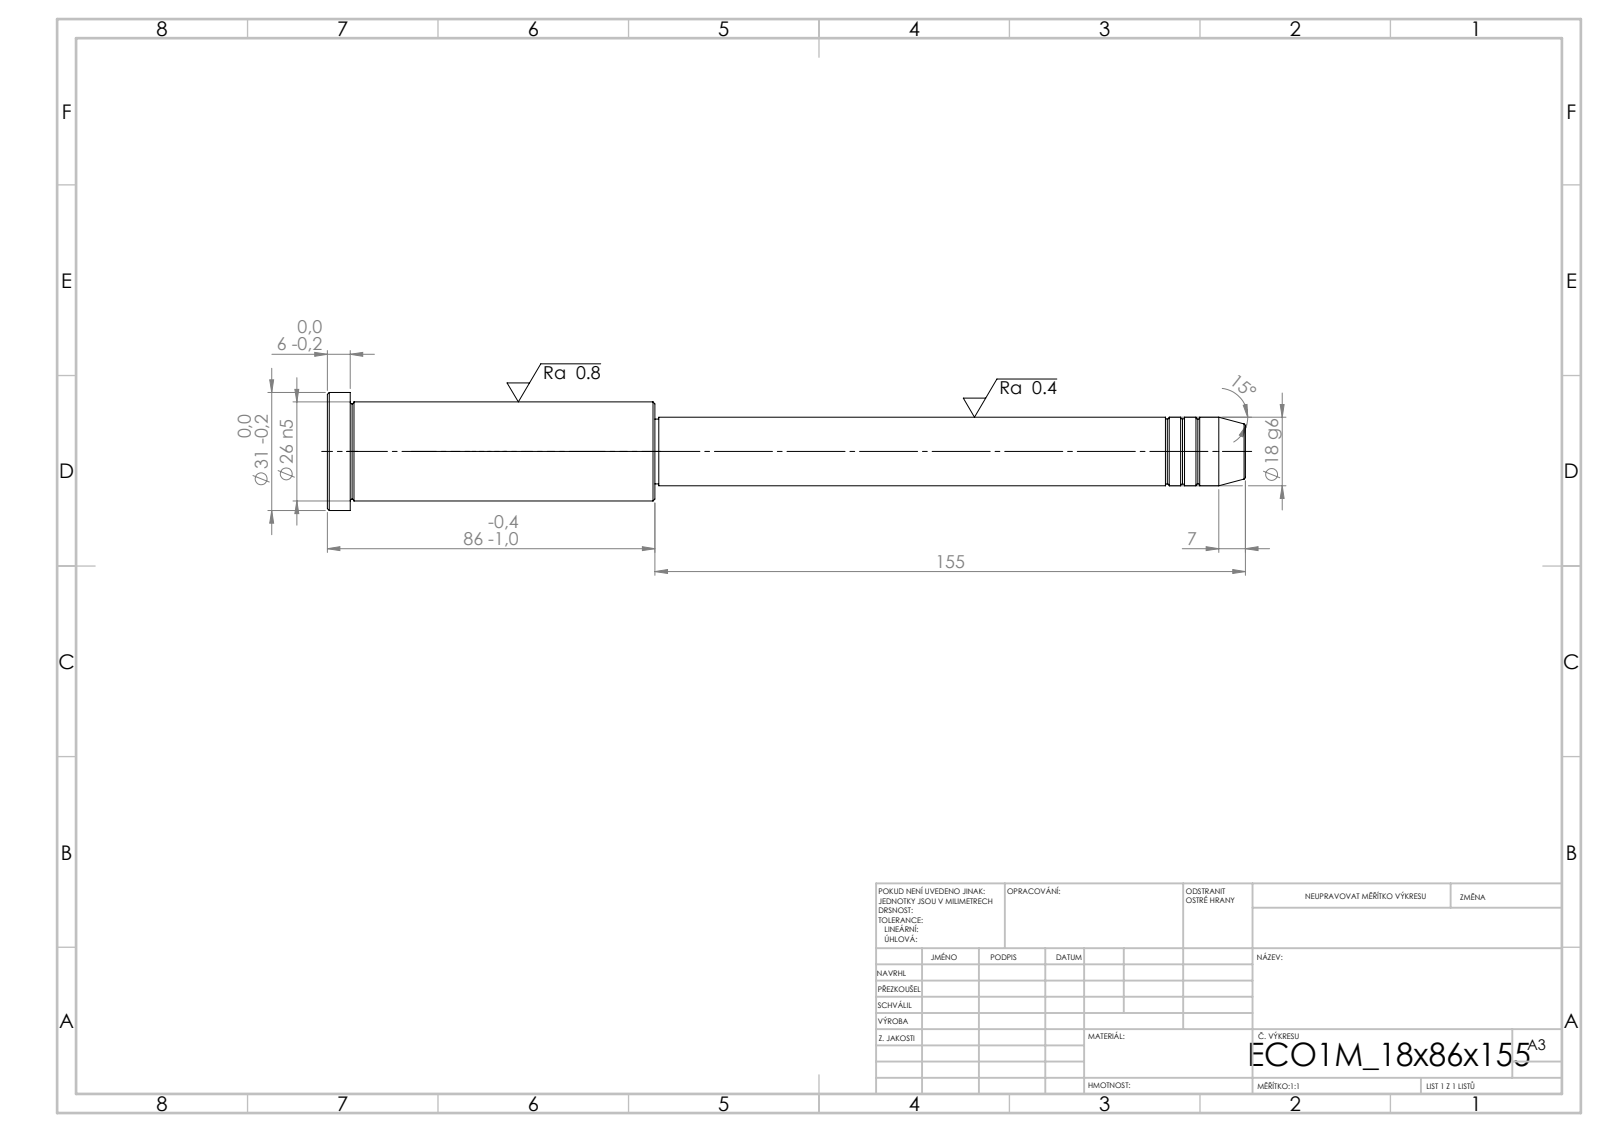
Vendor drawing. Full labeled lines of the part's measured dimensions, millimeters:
STEP written by: SolidWorks 2019 (CONFIG_CONTROL_DESIGN)
Units: millimetres
Bodies: 1 solid, 43 faces (5 planar, 14 cylindrical, 24 other)
Overall size (bounding box): 241 × 31 × 31
Volume: 85 953 mm³ · Surface area: 17 394 mm²
Round bosses / shafts (diameter × count): ⌀31 ×1, ⌀26 ×1, ⌀18 ×1, ⌀17 ×1
Main face-to-face distances: 86, 80, 6, 155, 235, 241, 154, 1, 81, 87
